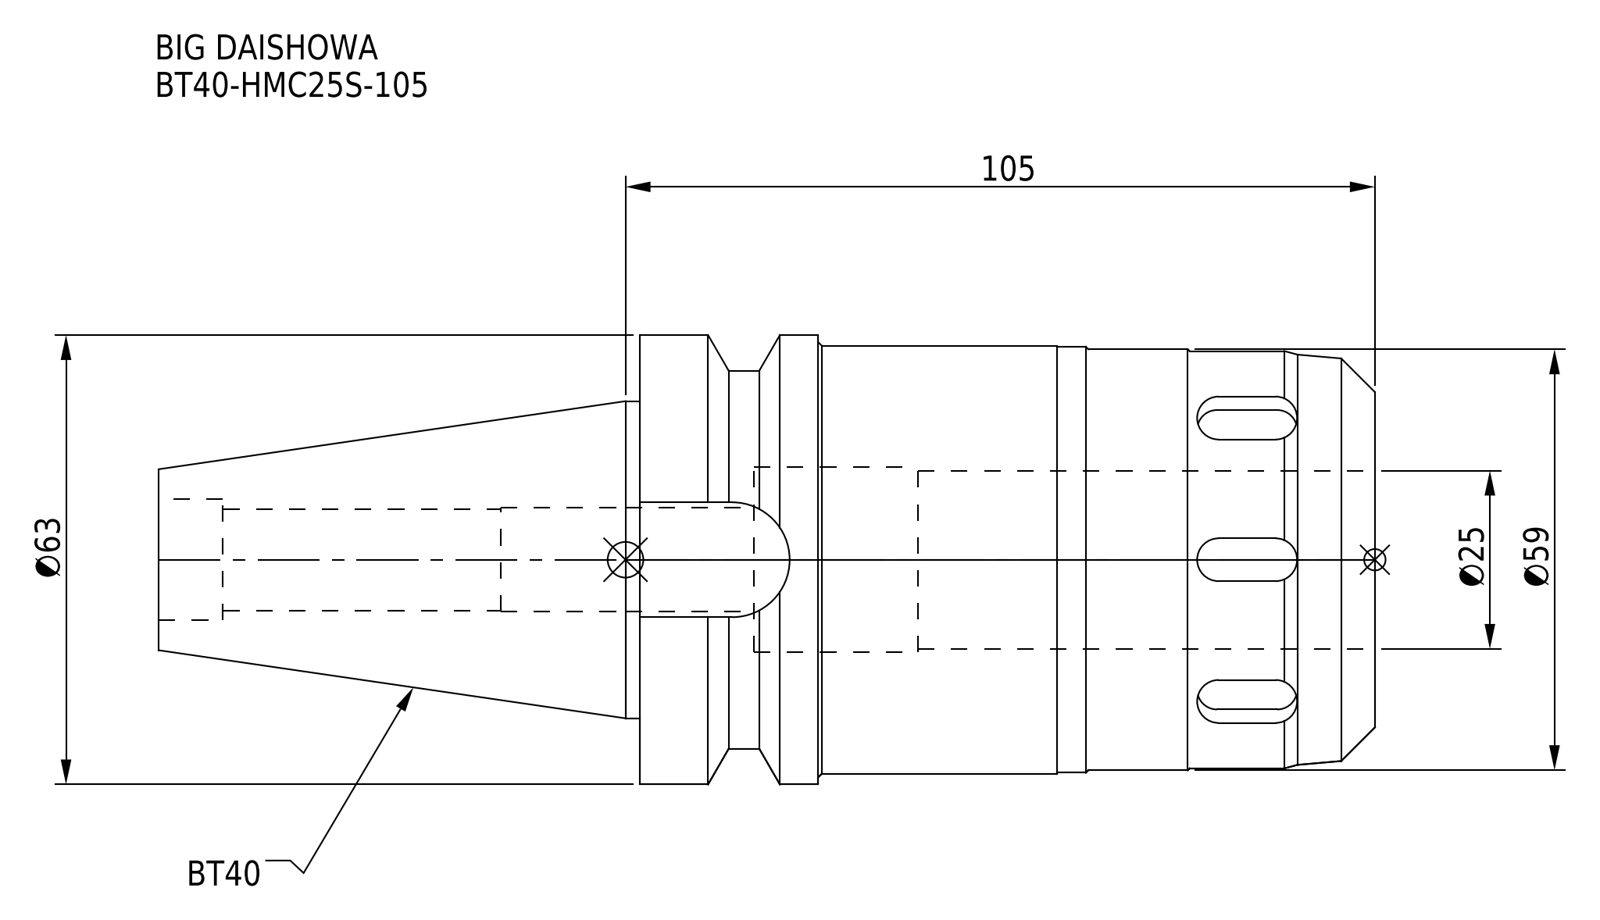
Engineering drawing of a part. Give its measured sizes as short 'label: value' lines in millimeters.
name: BT40-HMC25S-105
written by: CREO PARAMETRIC BY PTC INC, 2016380 (AUTOMOTIVE_DESIGN)
unit: mm
bodies: 1 solid, 101 faces (39 planar, 44 cylindrical, 18 other)
size: 170.4 × 63 × 63
volume: 287 059 mm³; area: 43 458 mm²
holes: 1× ⌀14.2, 1× ⌀14.5, 1× ⌀17, 1× ⌀25, 1× ⌀26
bosses: 1× ⌀63, 1× ⌀60, 1× ⌀59.7, 1× ⌀59, 1× ⌀58.5, 1× ⌀53, 1× ⌀44.45
rounds: 12× R3, 1× R8.05
face distances: 103, 87, 16, 83.4, 45, 54, 170.4, 67.4, 24, 30
